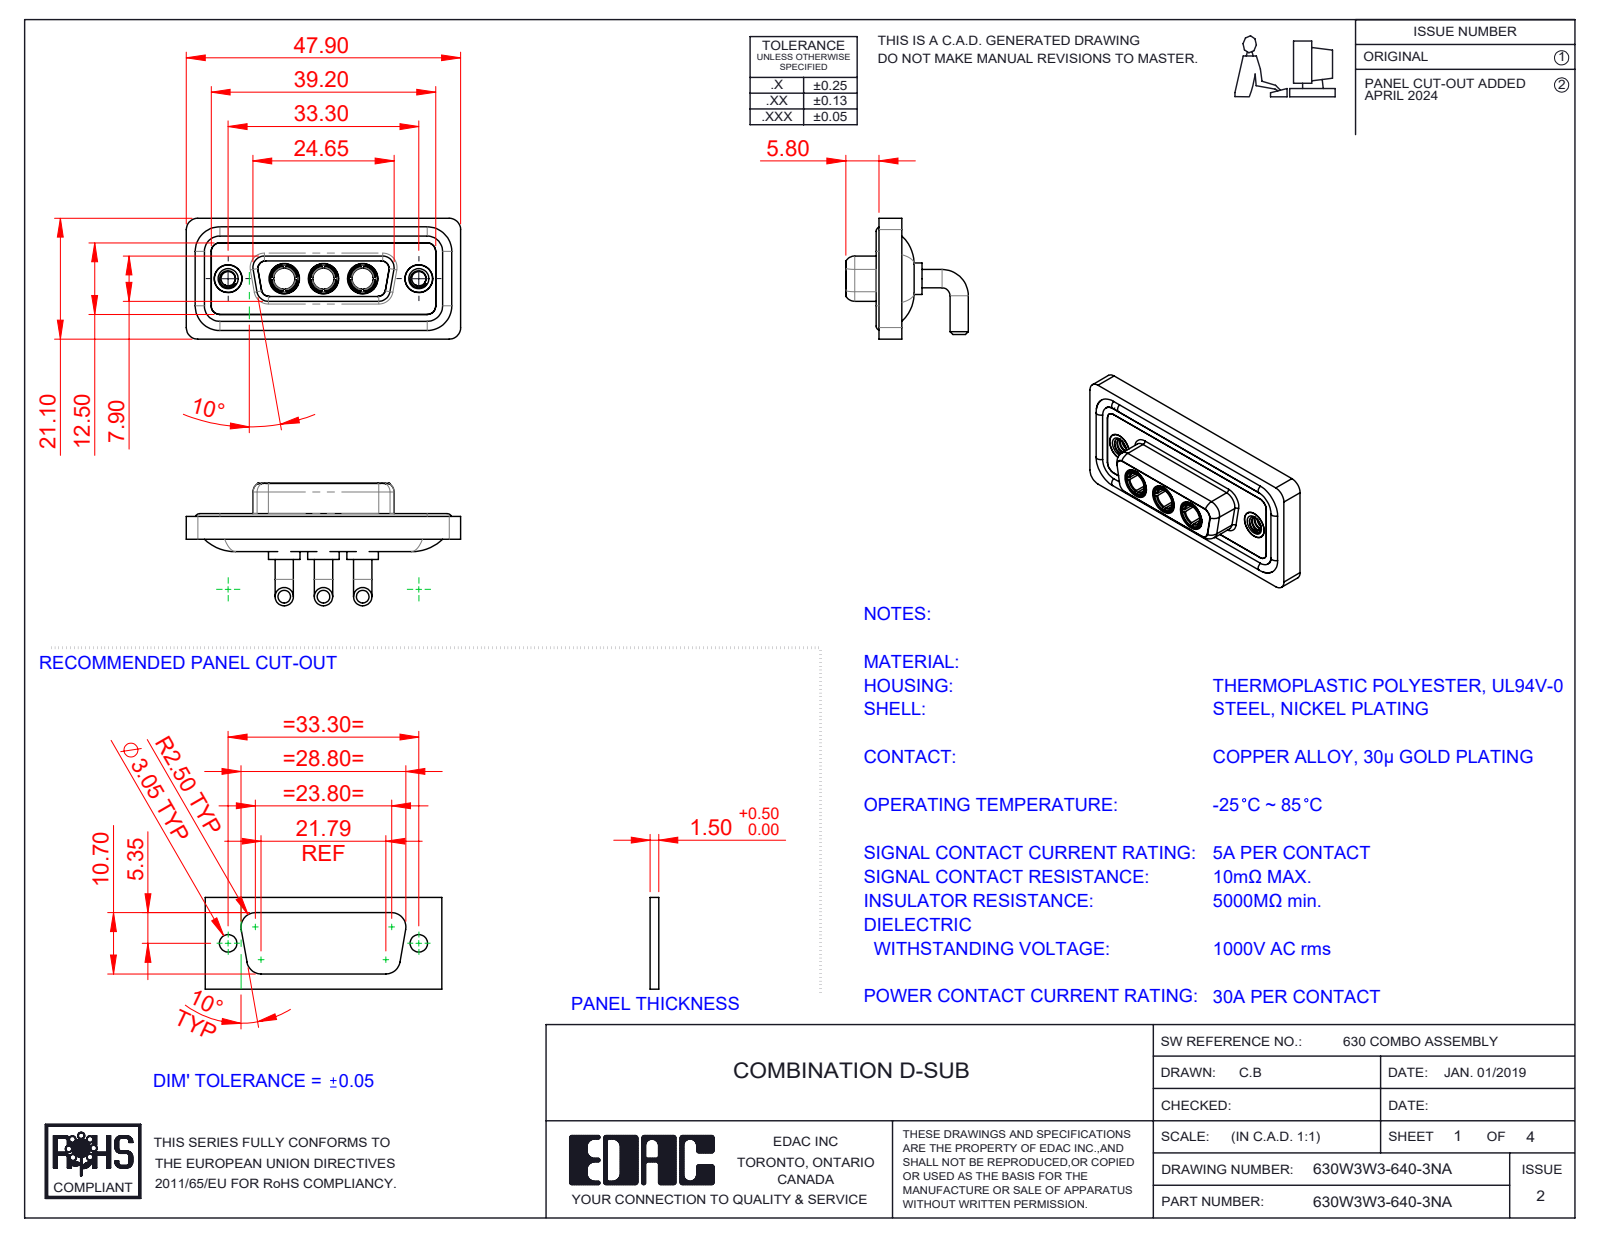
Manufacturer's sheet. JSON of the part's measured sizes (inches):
{"part_name": "630W3W3-640-3NA; Power Socket_30A RA; 630Combo Housing_3W3; 630Combo Shell Front_15 Contacts (+3 more)", "step_written_by": "SolidWorks 2023 (CONFIG_CONTROL_DESIGN)", "units": "inches", "bodies": {"solids": 13, "faces": 614, "planar": 192, "cylindrical": 261, "other": 161}, "overall_size": [1.886, 0.843, 0.831], "volume_in3": 0.382, "surface_area_in2": 15.55, "round_holes": [[0.191, 5], [0.146, 3], [0.209, 3], [0.098, 2], [0.157, 2], [0.159, 2], [0.197, 2]], "round_bosses_or_shafts": [[0.126, 6], [0.063, 4], [0.217, 3], [0.205, 3], [0.195, 3], [0.187, 3], [0.148, 3], [0.195, 2]], "partial_cylinders_radius": [[0.079, 20], [0.059, 18], [0.053, 12], [0.063, 8], [0.01, 4], [0.02, 4], [0.024, 4], [0.026, 4]], "face_to_face_distances": [0.016, 0.071, 0.043, 0.063, 0.114, 0.098, 0.122, 0.146, 0.161, 0.059], "hole_center_spacings": [0.27, 0.386, 0.656, 0.925, 0.539, 1.311]}
